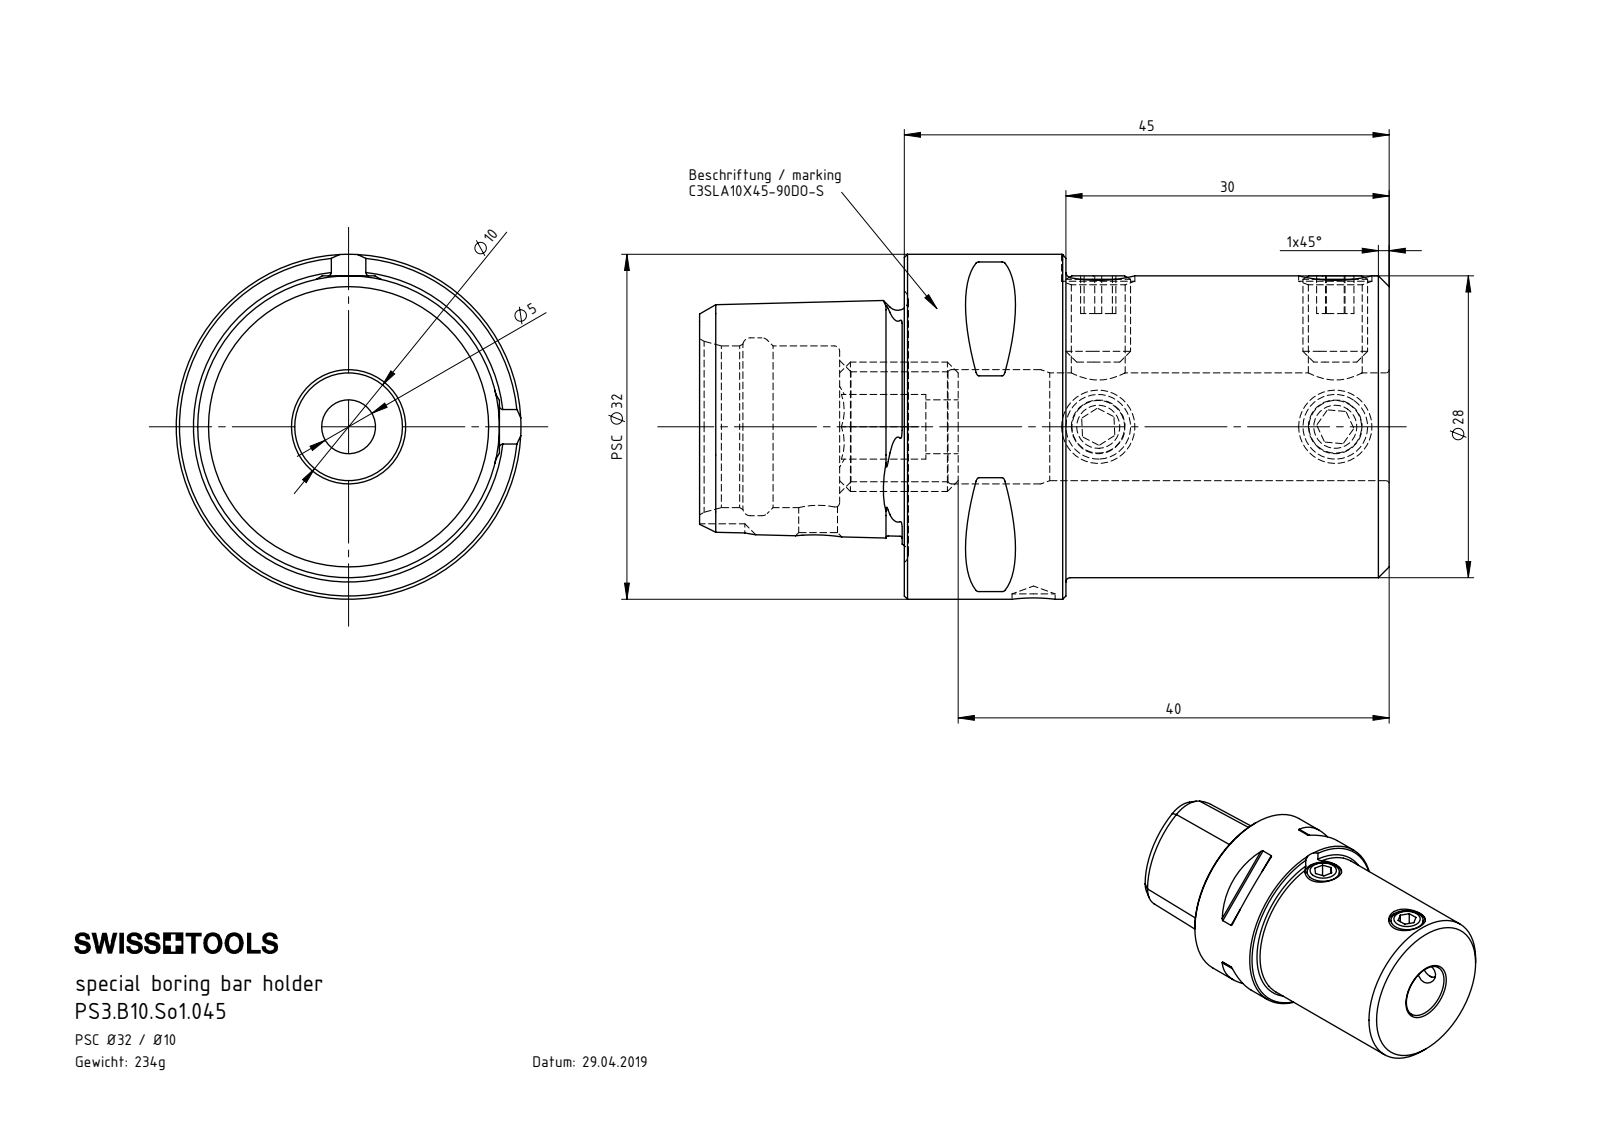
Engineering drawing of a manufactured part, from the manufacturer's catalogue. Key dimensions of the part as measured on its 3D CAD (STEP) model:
Part name (STEP PRODUCT): ISO 4026 - M6 x 8; PS3.B10.So1.045; ER1.PS3.012.011_A; PS3-B10.So1.045_A
STEP written by: SolidWorks 2017 (AUTOMOTIVE_DESIGN)
Units: millimetres
Bodies: 6 solids, 244 faces (66 planar, 57 cylindrical, 121 other)
Overall size (bounding box): 64 × 32 × 32
Volume: 31 304 mm³ · Surface area: 11 145 mm²
Round holes (diameter × count): ⌀5 ×5, ⌀6.8 ×4, ⌀3.6 ×1, ⌀4 ×1, ⌀10 ×1, ⌀10.2 ×1, ⌀10.6 ×1, ⌀15 ×1, ⌀16.5 ×1
Round bosses / shafts (diameter × count): ⌀6 ×4, ⌀32 ×1, ⌀28 ×1, ⌀12 ×1
Partial cylindrical surfaces — rounded edges, fillets, slot ends (radius × count): R0.3 ×8, R3 ×1
Main face-to-face distances: 45, 6, 15, 30, 3, 19, 34, 64, 13, 21
Hole centre spacings: 22, 6, 20, 26, 28, 48
